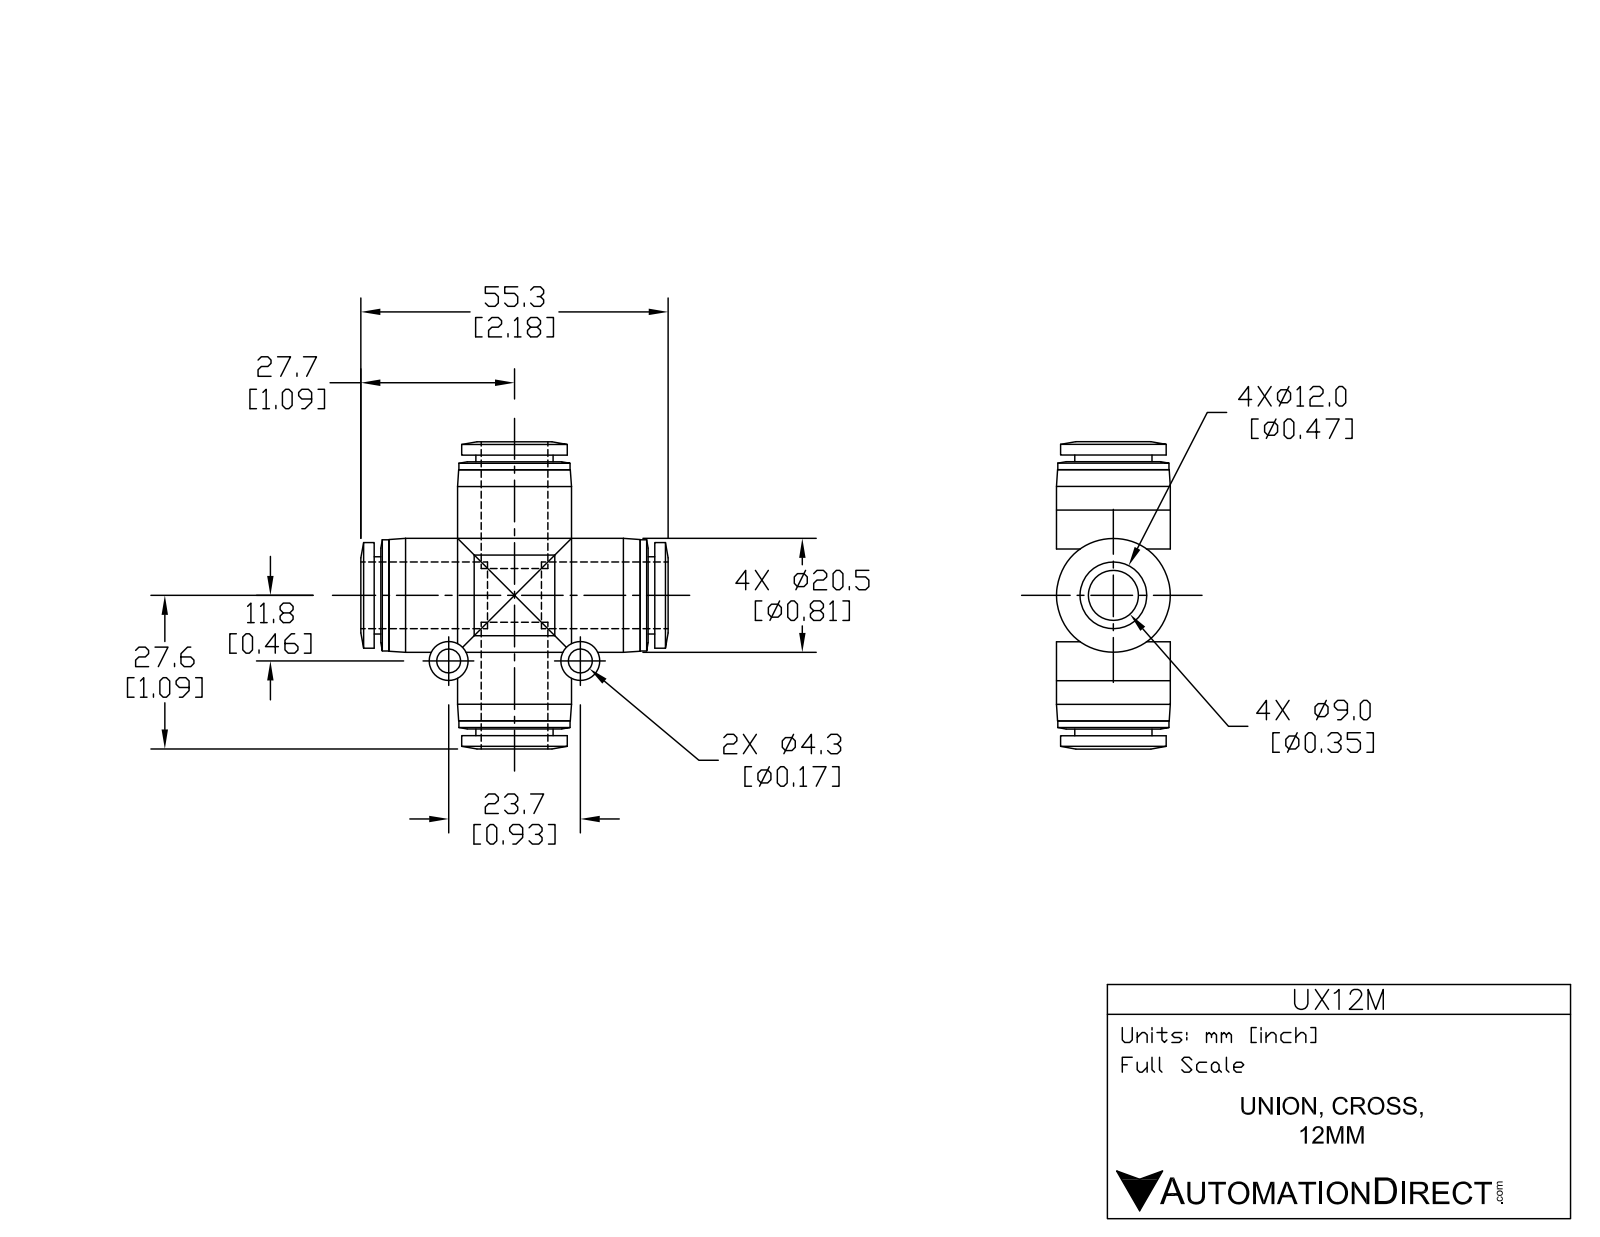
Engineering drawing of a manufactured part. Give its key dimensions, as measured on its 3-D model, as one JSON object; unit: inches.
{"part_name": "UX12M", "step_written_by": "SolidWorks 2018 (AUTOMOTIVE_DESIGN)", "units": "inches", "bodies": {"solids": 1, "faces": 132, "planar": 28, "cylindrical": 64, "other": 40}, "overall_size": [2.272, 2.177, 0.807], "volume_in3": 1.034, "surface_area_in2": 19.33, "round_holes": [[0.169, 2], [0.394, 2], [0.484, 2]], "round_bosses_or_shafts": [[0.807, 2], [0.787, 2], [0.748, 2], [0.571, 2], [0.547, 2], [0.276, 2]], "face_to_face_distances": [0.047, 1.988, 2.035, 0.787, 0.74, 2.083, 1.941, 0.094, 2.177, 0.142], "hole_center_spacings": [0.933]}
